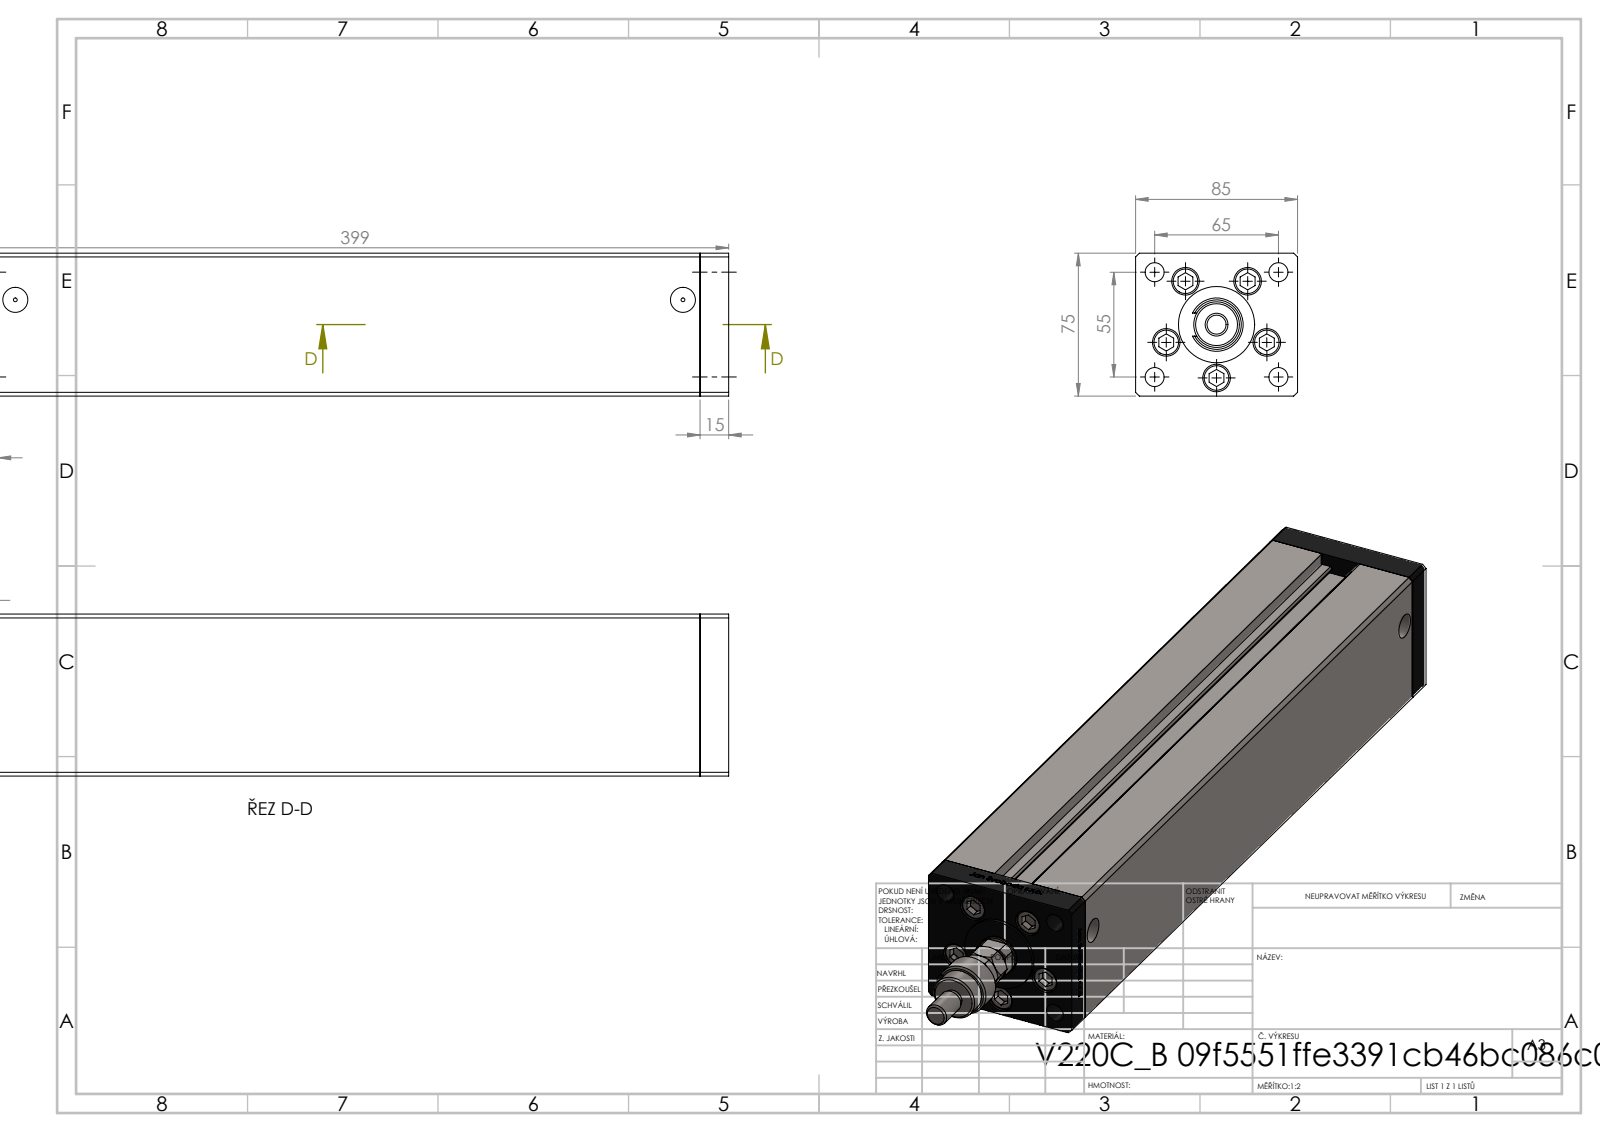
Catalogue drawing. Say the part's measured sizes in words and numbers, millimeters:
The part is named "FEMALE_PART_FOR_DFA; ALLEN BOLT; V220C_B MIDDLE; V220C BACK_B (+3 more)". Its 3-D file was written by "SolidWorks 2019 (CONFIG_CONTROL_DESIGN)". It is 16 solids with 1268 faces: 490 planar, 160 cylindrical and 618 other. Overall it measures 471 by 85 by 75 millimeters. Its volume is 2 195 000 cubic millimeters and its surface area 285 143 square millimeters. Round holes: 5 of diameter 11, 5 of diameter 14.5, 4 of diameter 10, 2 of diameter 2, 2 of diameter 13.16, 1 of diameter 13.5, 1 of diameter 22. Round bosses or shafts: 5 of diameter 8, 1 of diameter 40, 1 of diameter 28, 1 of diameter 24, 1 of diameter 18, 1 of diameter 12, 1 of diameter 11, 1 of diameter 10. Partial cylindrical surfaces (rounded edges, fillets, slot ends): 2 of radius 0.93, 1 of radius 9.75, 1 of radius 10.5. The main face-to-face distances are 85, 75, 15, 368.5, 383.5, 64.5, 10.5, 31.25, 53.75, 68.5. The hole center spacings are 28, 42.57, 16.86, 19.17, 32.33, 32.5, 33.63, 37.33.
